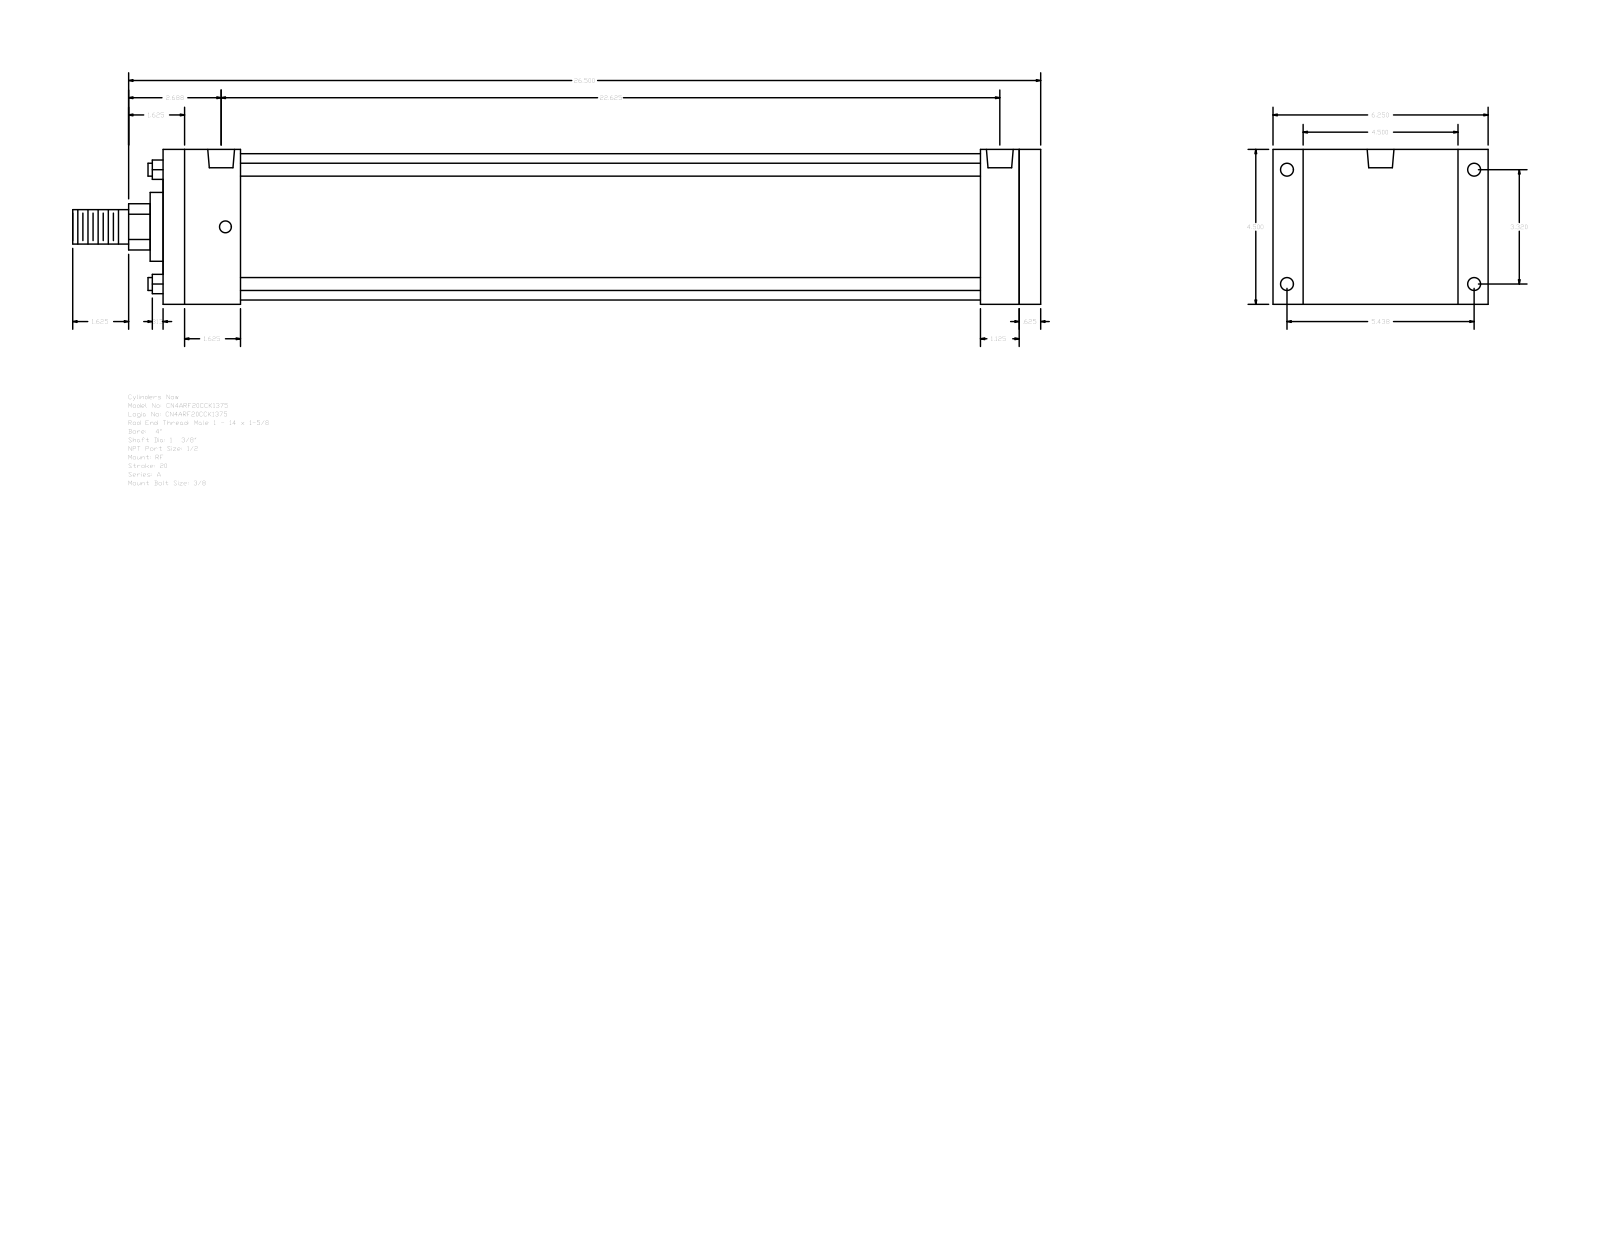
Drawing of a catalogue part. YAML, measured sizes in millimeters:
part_name: "A_RF__0400_1.375"
step_written_by: "GSSL Pune (CONFIG_CONTROL_DESIGN)"
units: millimeters
bodies: {solids: 0, faces: 92, planar: 64, cylindrical: 28, other: 0}
overall_size: [714.38, 158.75, 114.3]
round_holes:
  - {diameter: 8.73, count: 4}
  - {diameter: 9.53, count: 4}
  - {diameter: 19.77, count: 2}
round_bosses_or_shafts:
  - {diameter: 9.53, count: 4}
  - {diameter: 107.95, count: 1}
  - {diameter: 50.8, count: 1}
  - {diameter: 34.92, count: 1}
  - {diameter: 25.4, count: 1}
partial_cylinders:
  - {radius: 17.06, count: 1}
face_to_face_distances: [114.3, 647.7, 631.83, 15.87, 57.15, 28.58, 22.23, 136.53, 603.25, 44.45]
hole_center_spacings: [3.18, 84.32, 138.12, 161.82, 568.32, 571.5, 574.68]
